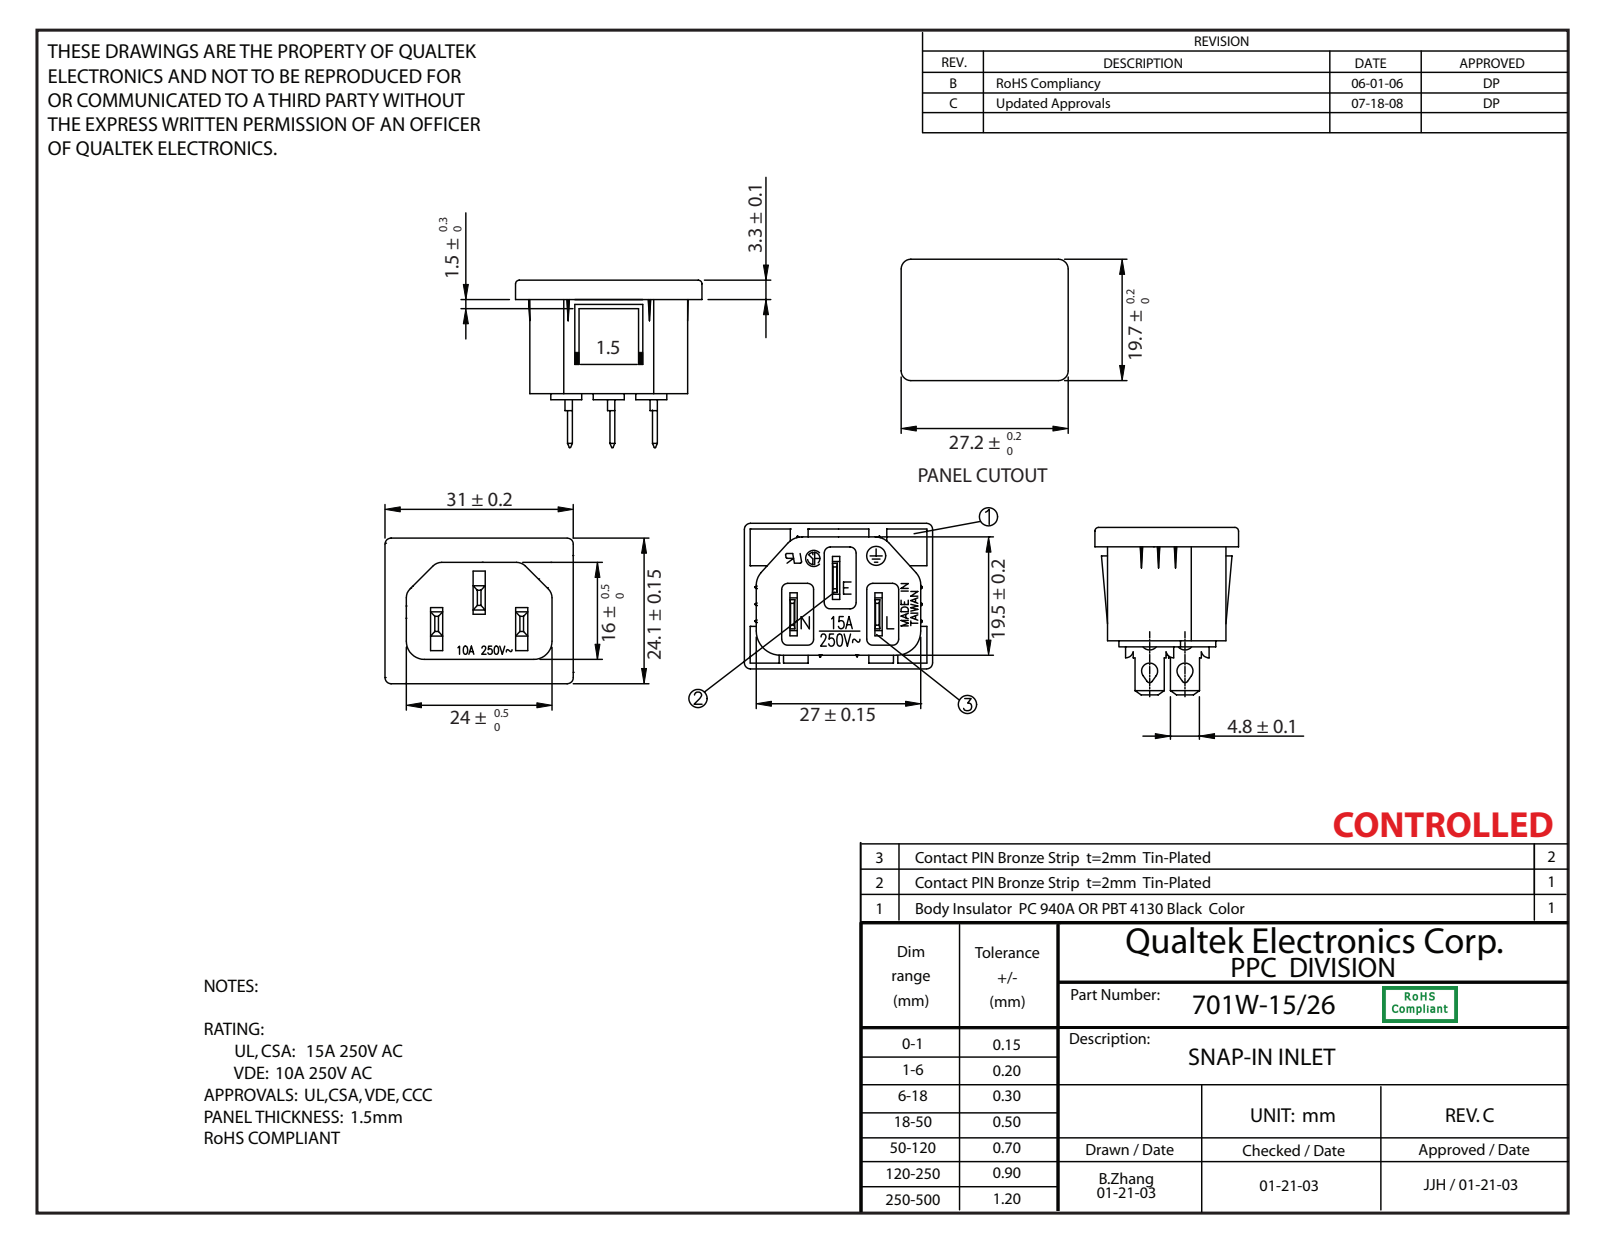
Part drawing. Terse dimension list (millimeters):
name: 701W
written by: SolidWorks 2010 (AUTOMOTIVE_DESIGN)
unit: mm
bodies: 4 solids, 263 faces (209 planar, 50 cylindrical, 4 other)
size: 31 × 27.3 × 24
volume: 4 262 mm³; area: 5 793 mm²
holes: 2× ⌀2
rounds: 16× R1, 4× R0.8, 4× R1.5, 4× R3, 2× R0.5, 2× R1.3, 2× R2.5, 2× R4
face distances: 2, 7, 16.5, 14.5, 2.3, 14, 7.5, 21.5, 18.8, 1.2
hole spacings: 5.81
